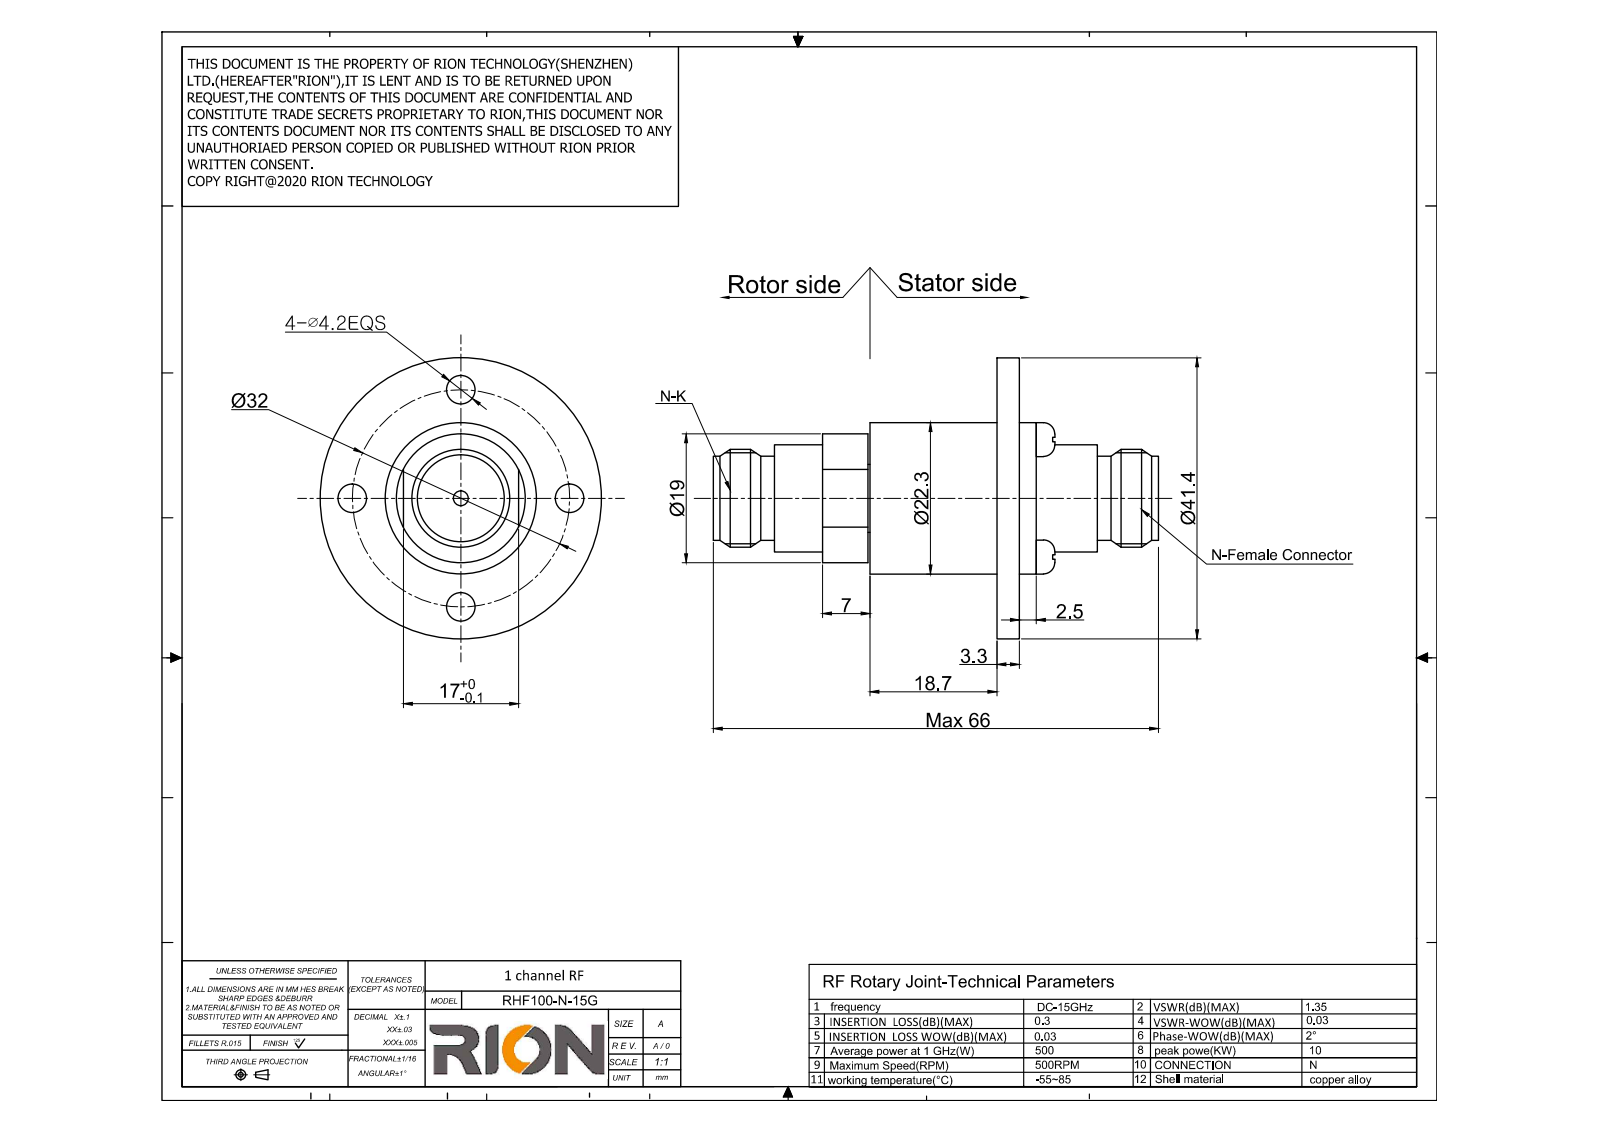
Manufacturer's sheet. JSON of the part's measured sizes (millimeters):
{"part_name": "RHF100-N-15G", "step_written_by": "SolidWorks 2014 (AUTOMOTIVE_DESIGN)", "units": "millimeters", "bodies": {"solids": 1, "faces": 60, "planar": 14, "cylindrical": 38, "other": 8}, "overall_size": [65.6, 41.4, 41.4], "volume_mm3": 20622, "surface_area_mm2": 7320, "round_holes": [[4.2, 4], [2.2, 1]], "round_bosses_or_shafts": [[41.4, 1], [22.3, 1], [15.8, 1], [13.8, 1], [10, 1]], "partial_cylinders_radius": [[9.5, 1]], "face_to_face_distances": [3.3, 18.7, 22, 24.5, 5.8, 2.5, 19, 22.3, 24.8, 47.6], "hole_center_spacings": [16, 22.63, 32]}
